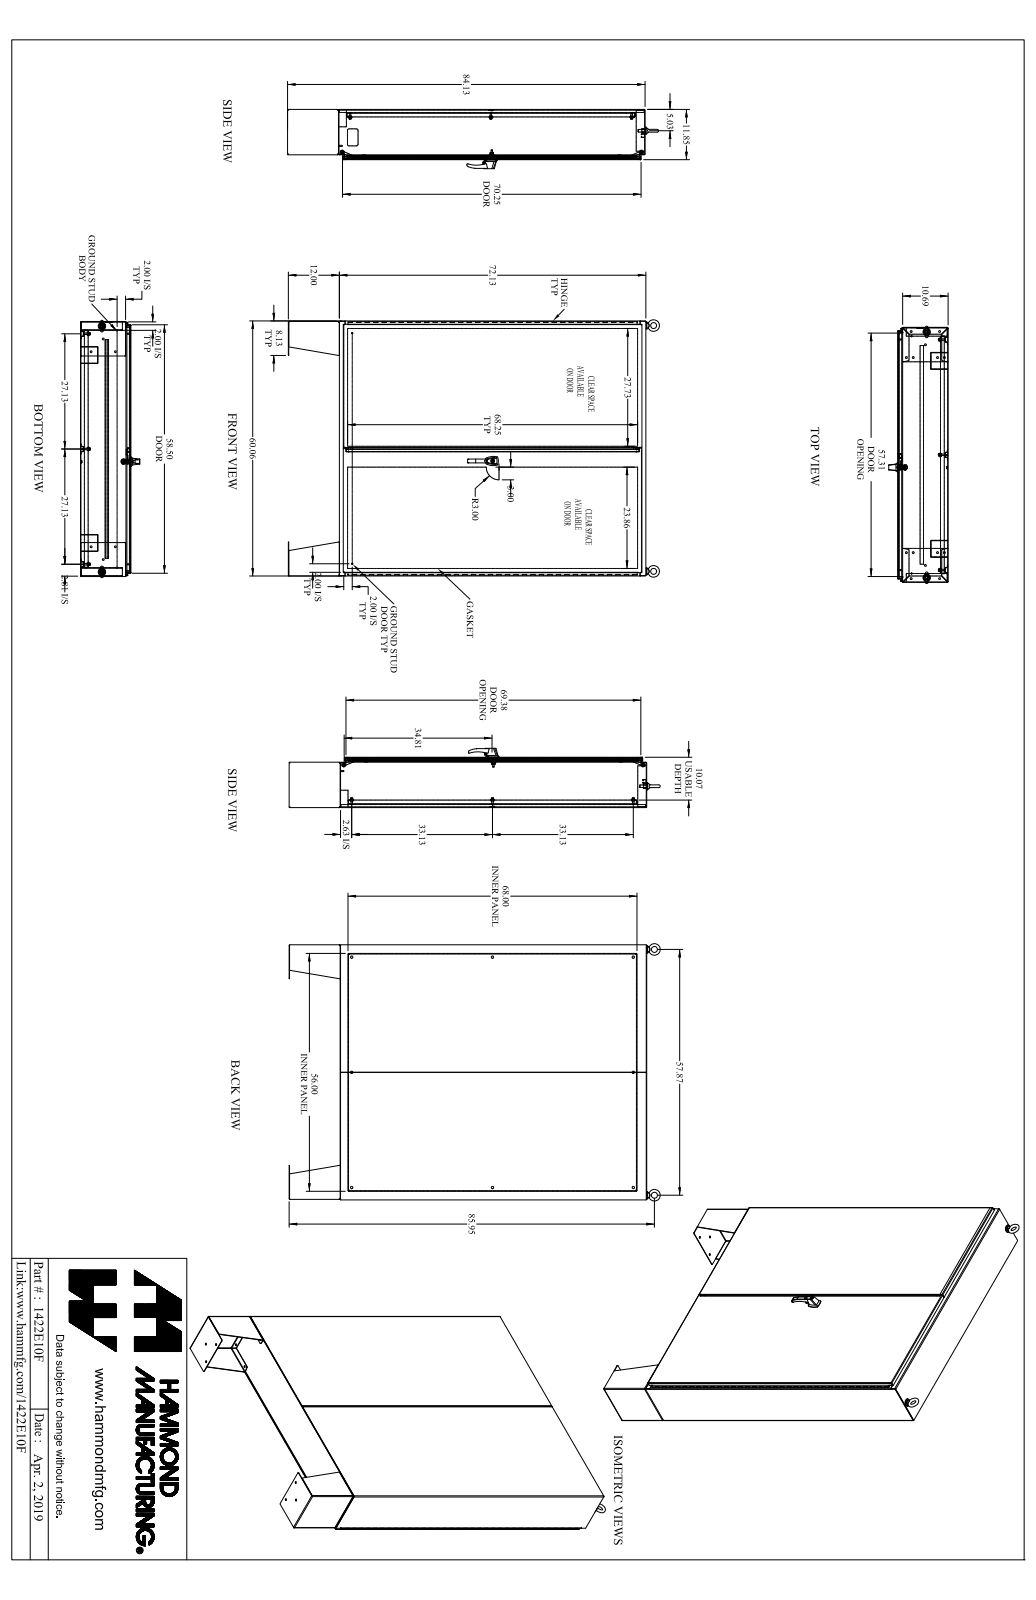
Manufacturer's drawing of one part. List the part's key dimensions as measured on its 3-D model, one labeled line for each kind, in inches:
Part name (STEP PRODUCT): 1422E10F_Default
STEP written by: SolidWorks 2019 (CONFIG_CONTROL_DESIGN)
Units: inches
Bodies: 92 solids, 2997 faces (1372 planar, 1378 cylindrical, 247 other)
Overall size (bounding box): 87.778 × 61.121 × 13.963
Volume: 2 037 in³ · Surface area: 37 751 in²
Round holes (diameter × count): ⌀0.304 ×24, ⌀0.437 ×14, ⌀0.307 ×9, ⌀0.563 ×8, ⌀0.445 ×6, ⌀0.11 ×2, ⌀0.25 ×2, ⌀0.257 ×2, ⌀0.28 ×2, ⌀0.281 ×2, ⌀0.313 ×2, ⌀0.39 ×2
Round bosses / shafts (diameter × count): ⌀1 ×10, ⌀0.65 ×8, ⌀0.375 ×8, ⌀0.33 ×8, ⌀0.281 ×6, ⌀0.25 ×4, ⌀1.75 ×2, ⌀1.5 ×2
Partial cylindrical surfaces — rounded edges, fillets, slot ends (radius × count): R0.048 ×32, R0.143 ×32, R0.125 ×22, R0.018 ×16, R0.06 ×14, R0.116 ×12, R0.187 ×9, R0.05 ×8
Main face-to-face distances: 0.095, 0.125, 11.753, 11.628, 11.723, 11.848, 0.125, 10.036, 9.941, 1.687
Hole centre spacings: 6, 12, 58.7, 59.613, 18, 61.104, 24, 63.132
